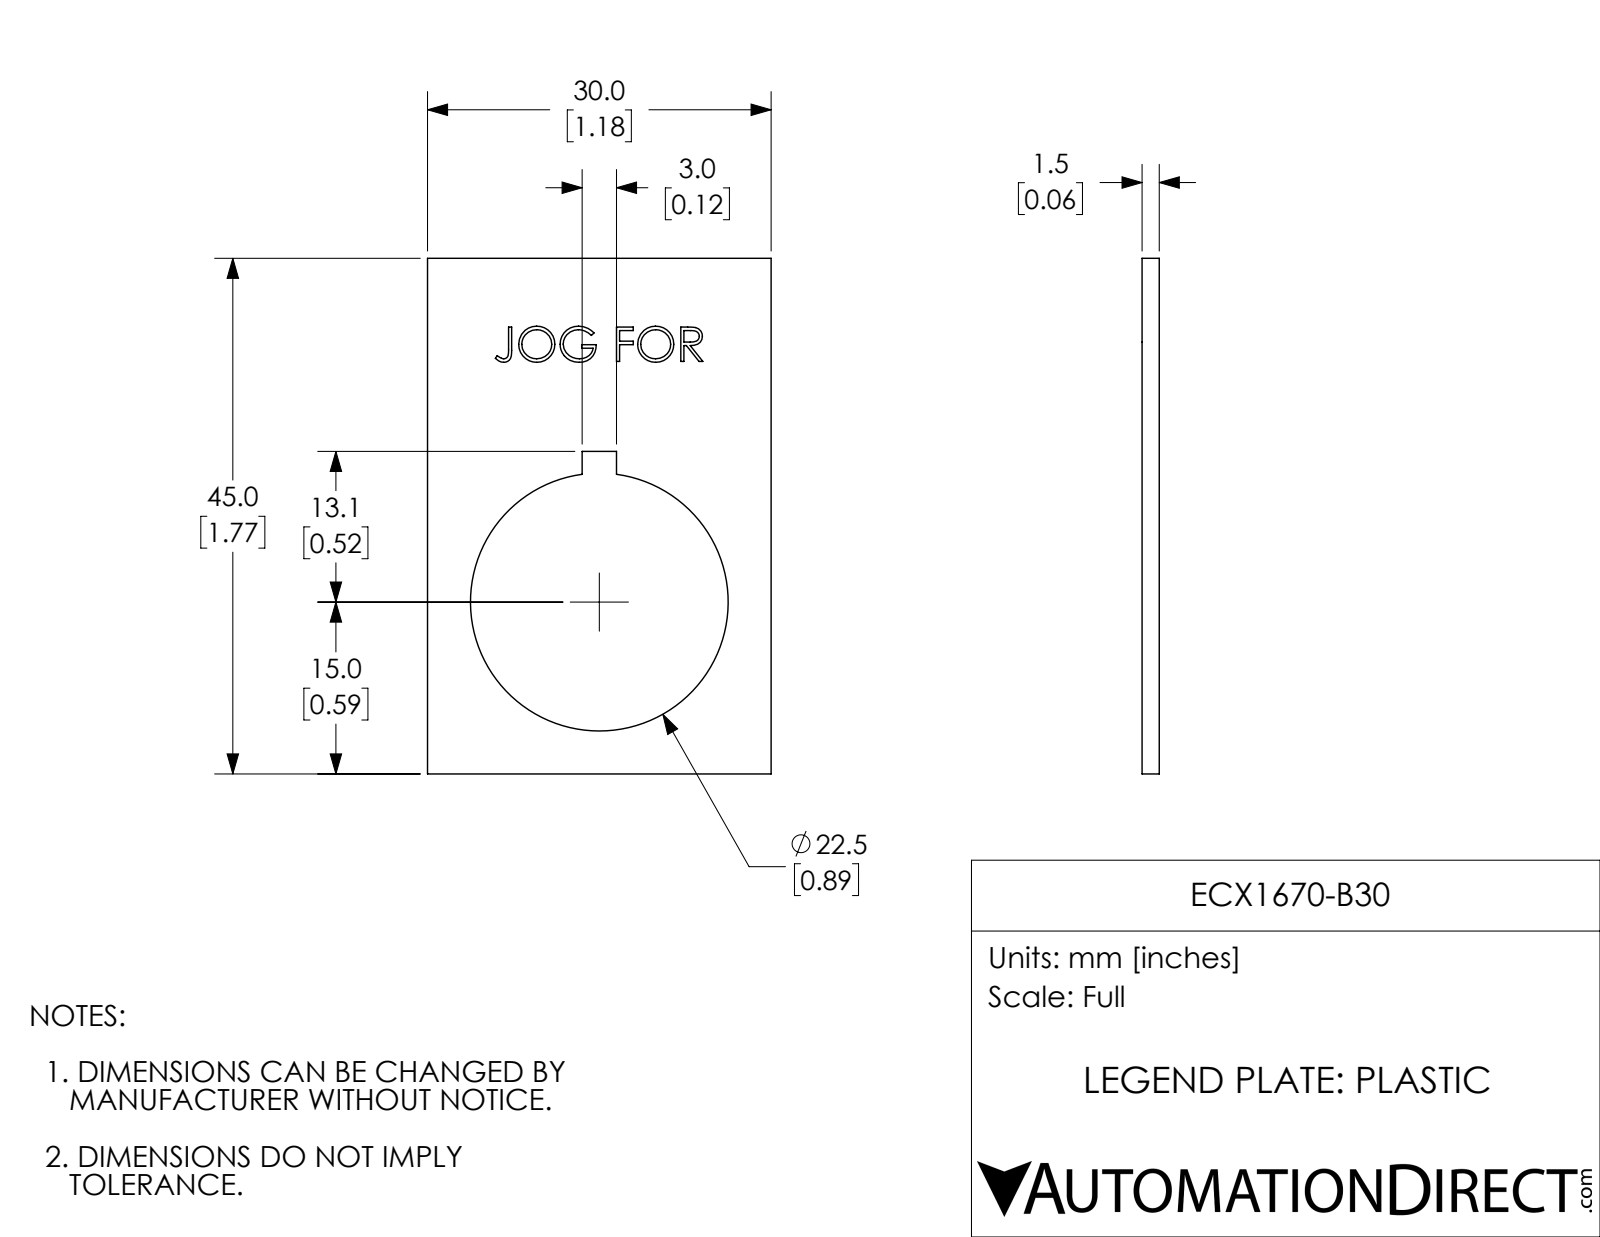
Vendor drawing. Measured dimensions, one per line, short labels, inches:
name: ECX1670-B30
written by: SolidWorks 2017 (AUTOMOTIVE_DESIGN)
unit: in
bodies: 1 solid, 85 faces (47 planar, 3 cylindrical, 35 other)
size: 1.772 × 1.181 × 0.059
volume: 0.087 in³; area: 3.461 in²
holes: 1× ⌀0.886
face distances: 0.059, 1.181, 1.772, 0.058, 0.531, 0.65, 1.108, 0.663, 0.118, 0.371
